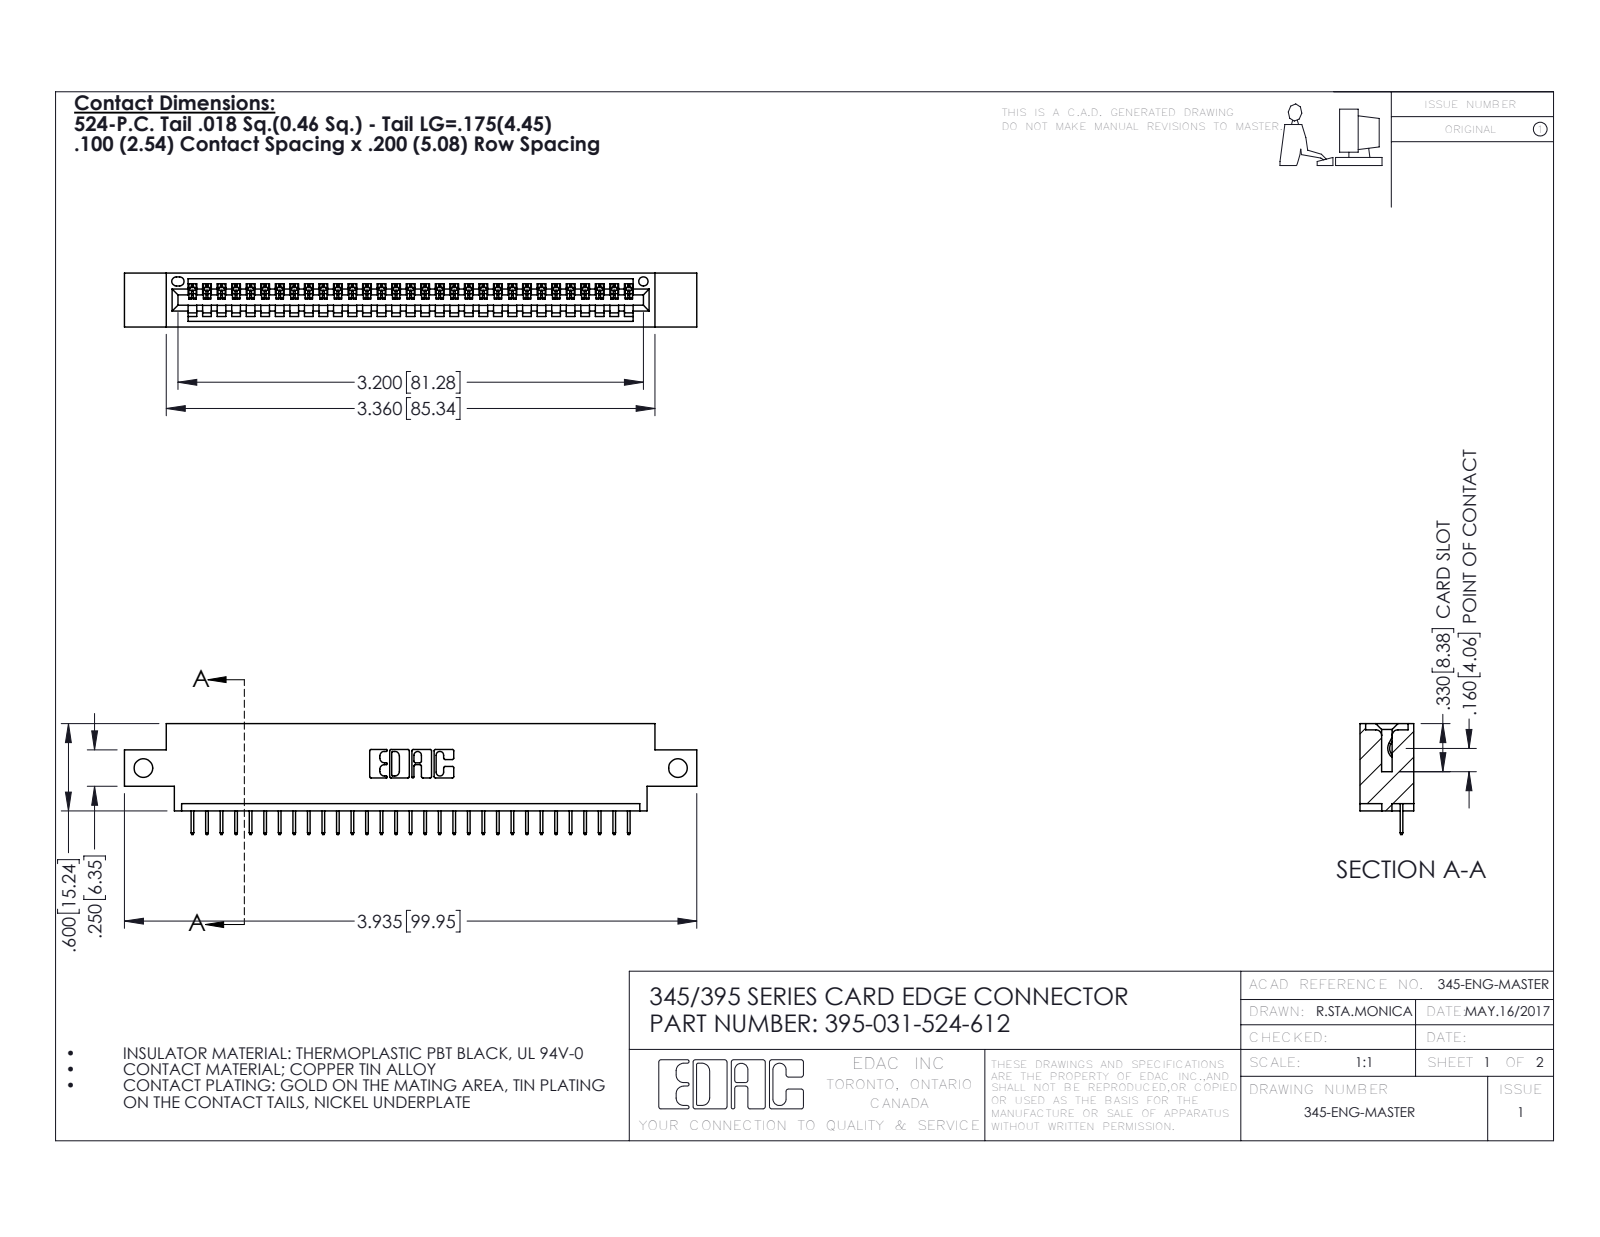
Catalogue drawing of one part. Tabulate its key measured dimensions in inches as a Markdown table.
| quantity | value |
| --- | --- |
| part name | 345 Part_0.170 Offset - Side Mount; 345-292-001_345-293-124; 395-031-524-612 |
| STEP written by | SolidWorks 2016 (CONFIG_CONTROL_DESIGN) |
| units | inches |
| bodies | 32 solids, 2052 faces (1510 planar, 542 cylindrical, 0 other) |
| overall size | 3.935 × 0.762 × 0.37 |
| volume | 0.554 in³ |
| surface area | 17.84 in² |
| round holes (diameter × count) | 0.128 × 2, 0.064 × 1 |
| partial cylindrical surfaces (radius × count) | 0.006 × 62, 0.01 × 22, 0.007 × 6, 0.031 × 6, 0.026 × 3, 0.031 × 2, 0.04 × 2, 0.014 × 1 |
| main face-to-face distances | 0.072, 0.298, 0.37, 0.2, 0.098, 0.272, 0.025, 0.225, 0.072, 0.175 |
| hole center spacings | 3.675 |
